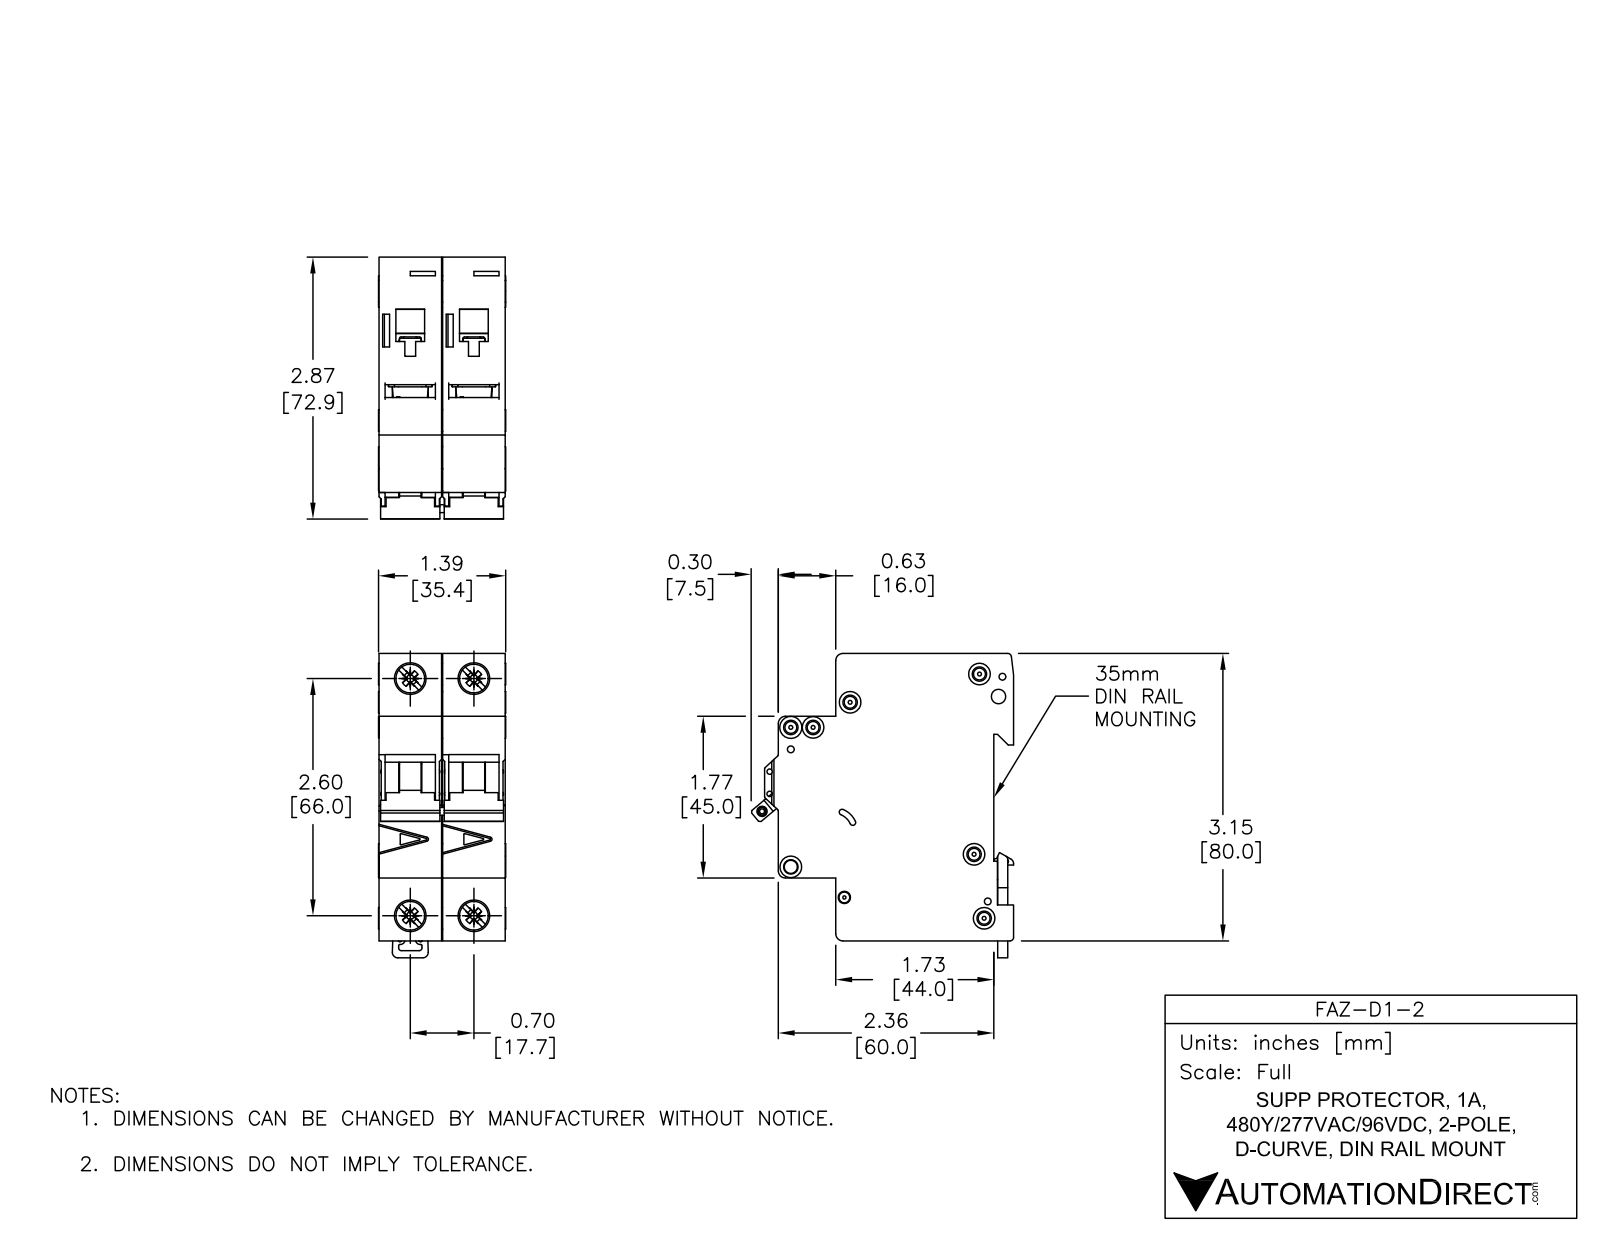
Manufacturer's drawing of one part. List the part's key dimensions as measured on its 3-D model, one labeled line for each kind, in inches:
Part name (STEP PRODUCT): FAZ-D1-2
STEP written by: SolidWorks 2014 (AUTOMOTIVE_DESIGN)
Units: inches
Bodies: 8 solids, 1104 faces (466 planar, 396 cylindrical, 242 other)
Overall size (bounding box): 3.338 × 2.876 × 1.394
Volume: 9.142 in³ · Surface area: 60.14 in²
Round holes (diameter × count): ⌀0.142 ×6, ⌀0.075 ×3, ⌀0.043 ×2, ⌀0.059 ×2, ⌀0.157 ×2, ⌀0.281 ×2, ⌀0.323 ×2, ⌀0.085 ×1, ⌀0.087 ×1, ⌀0.1 ×1, ⌀0.13 ×1, ⌀0.134 ×1
Round bosses / shafts (diameter × count): ⌀0.236 ×4, ⌀0.323 ×2, ⌀0.098 ×2
Partial cylindrical surfaces — rounded edges, fillets, slot ends (radius × count): R0.01 ×49, R0.02 ×19, R0.079 ×10, R0.008 ×8, R0.039 ×8, R0.031 ×2, R0.071 ×2, R0.118 ×2
Main face-to-face distances: 0.697, 0.689, 1.386, 3.129, 0.217, 1.949, 1.732, 2.579, 2.362, 0.63
Hole centre spacings: 0.244, 0.537, 0.697, 2.598, 2.69, 0.189, 0.204, 0.221
